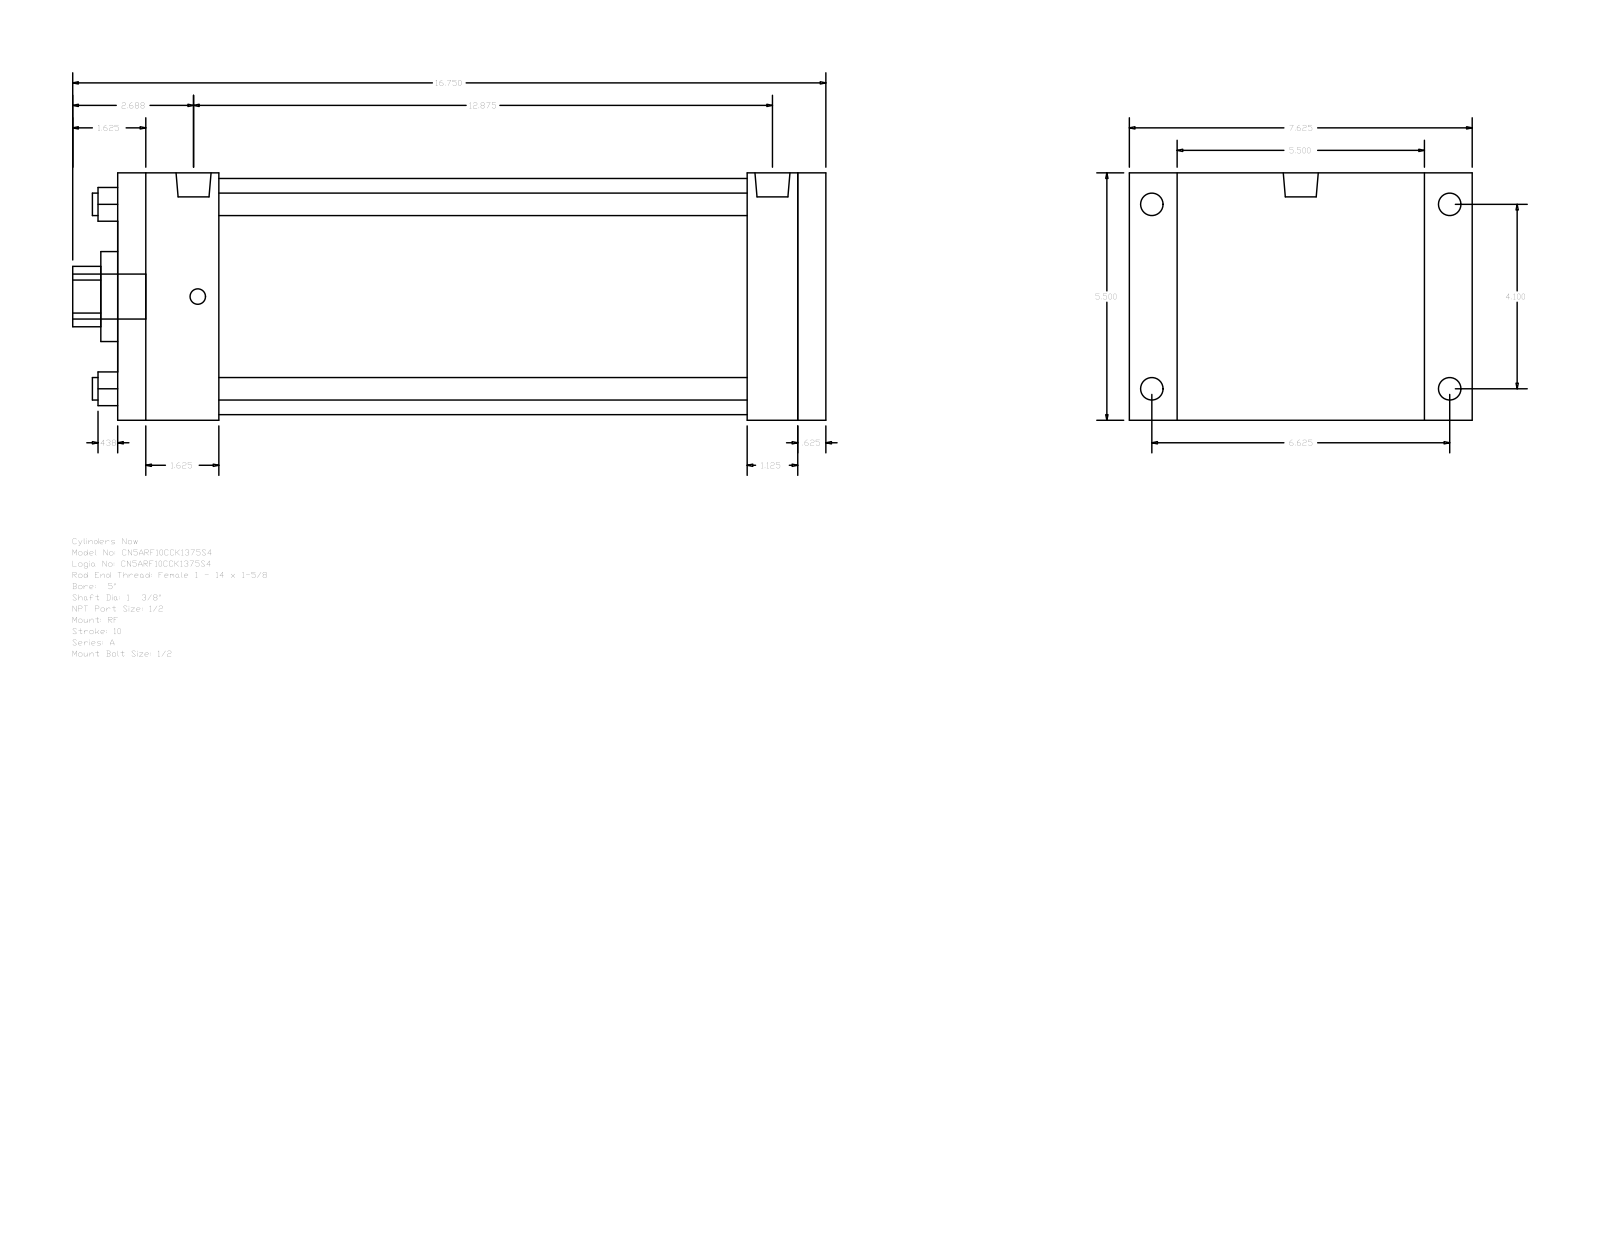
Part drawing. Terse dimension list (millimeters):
name: A_RF__0500_1.375
written by: GSSL Pune (CONFIG_CONTROL_DESIGN)
unit: mm
bodies: 0 solids, 92 faces (64 planar, 28 cylindrical, 0 other)
size: 425.45 × 193.68 × 139.7
holes: 4× ⌀12.7, 1× ⌀34.92, 1× ⌀50.8, 1× ⌀133.35
bosses: 4× ⌀12.7, 4× ⌀8.73, 2× ⌀19.77, 1× ⌀25.4
rounds: 1× R17.06
face distances: 139.7, 400.05, 15.88, 384.17, 28.57, 57.15, 327.02, 342.9, 355.6, 298.45
hole spacings: 73.64, 104.14, 147.28
